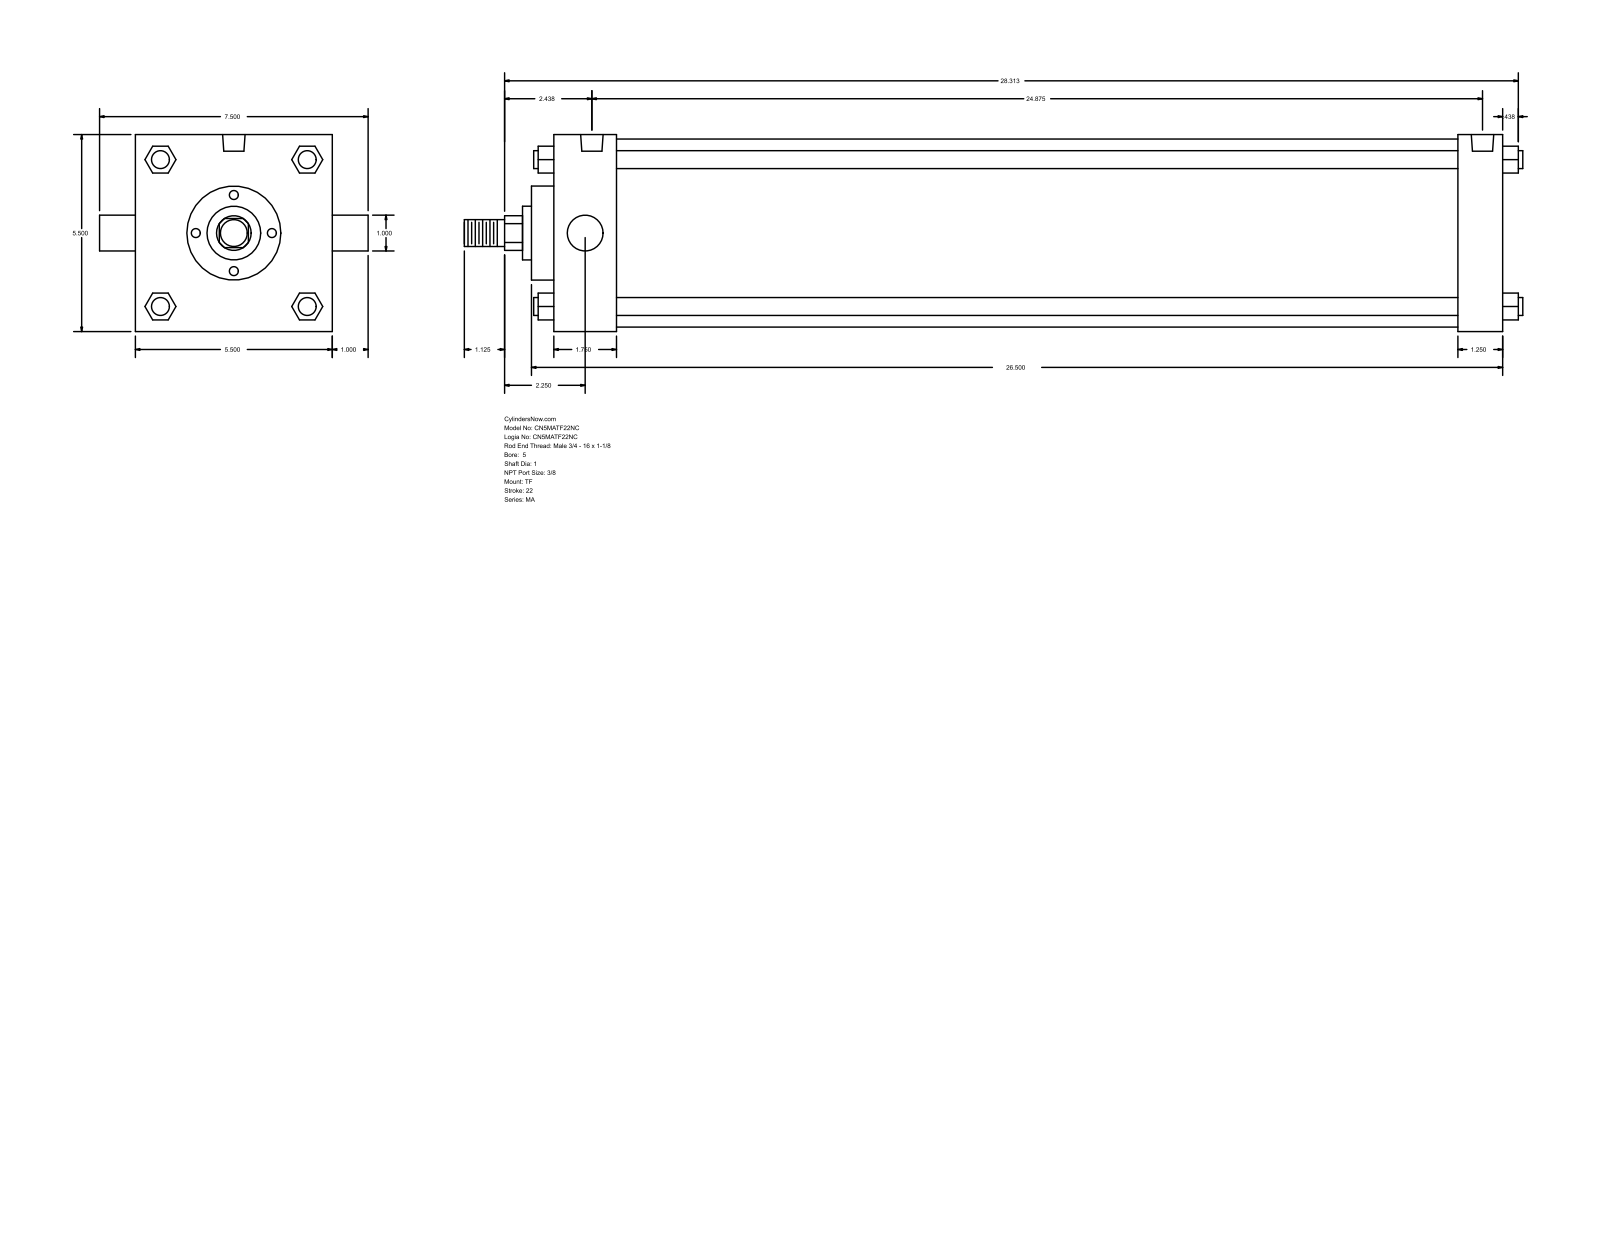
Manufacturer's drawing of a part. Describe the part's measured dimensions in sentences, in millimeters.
The part is named "MA_TF__0500_1". Its 3-D file was written by "GSSL Pune (CONFIG_CONTROL_DESIGN)". It is 0 solids with 122 faces: 93 planar, 29 cylindrical and 0 other. Overall it measures 750.89 by 190.5 by 139.7 millimeters. Round holes: 3 of diameter 11.11, 2 of diameter 15.93. Round bosses or shafts: 4 of diameter 12.7, 2 of diameter 25.4, 1 of diameter 133.35, 1 of diameter 66.67, 1 of diameter 38.1, 1 of diameter 19.05. Partial cylindrical surfaces (rounded edges, fillets, slot ends): 1 of radius 12.29. The main face-to-face distances are 139.7, 673.1, 641.35, 31.75, 44.46, 596.89, 628.64, 15.87, 60.33, 657.22. The hole center spacings are 4.76, 627.07, 622.31, 631.83.
